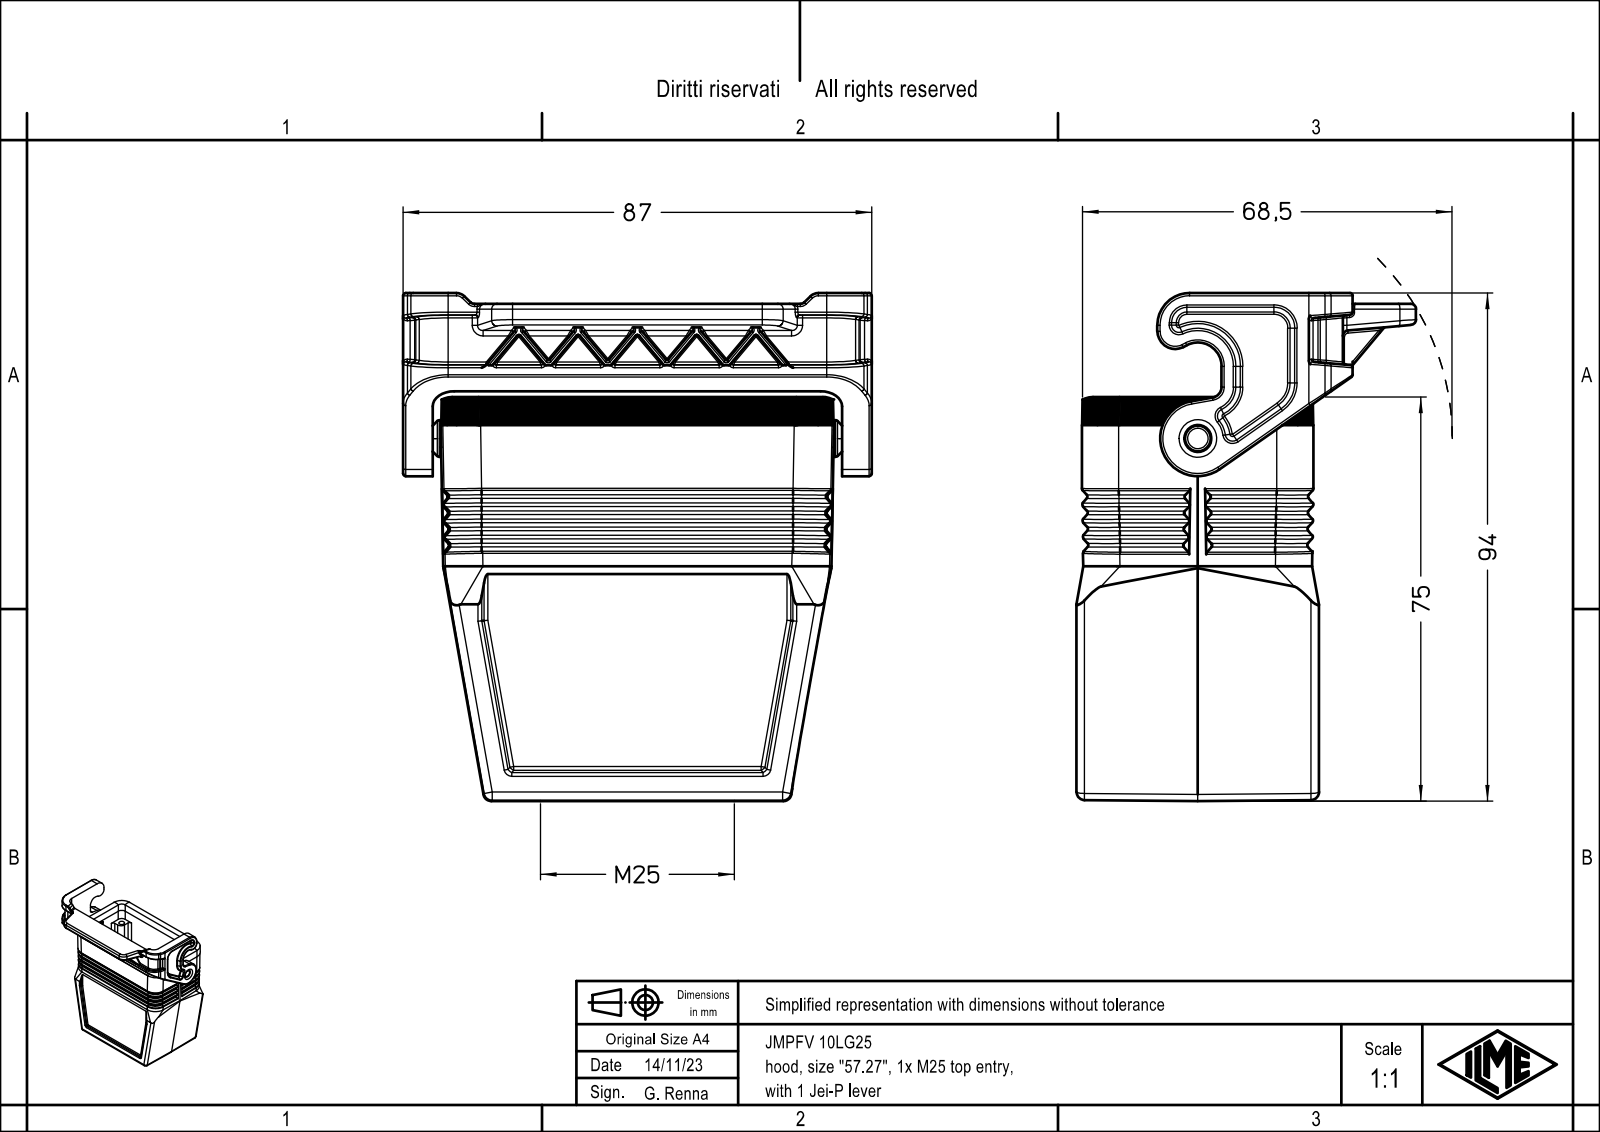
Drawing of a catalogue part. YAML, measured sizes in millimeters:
part_name: "JMPFV 10LG25"
step_written_by: "Creo Elements/Direct Modeling 20.1B 02-Apr-2019 (C) Parametric Technology GmbH (AUTOMOTIVE_DESIGN)"
units: millimeters
bodies: {solids: 1, faces: 998, planar: 269, cylindrical: 355, other: 374}
overall_size: [94.25, 87, 63]
volume: 88937
surface_area: 44343
round_holes:
  - {diameter: 3, count: 4}
  - {diameter: 3.5, count: 4}
  - {diameter: 4.8, count: 1}
  - {diameter: 23.6, count: 1}
round_bosses_or_shafts:
  - {diameter: 6.8, count: 1}
partial_cylinders:
  - {radius: 0.5, count: 96}
  - {radius: 0.3, count: 71}
  - {radius: 1, count: 35}
  - {radius: 1.5, count: 24}
  - {radius: 0.33, count: 15}
  - {radius: 7, count: 13}
  - {radius: 3, count: 12}
  - {radius: 4, count: 8}
face_to_face_distances: [39.25, 3.75, 43, 1, 4.75, 7, 34.5, 38.25, 35.5, 2]
hole_center_spacings: [31.54, 27, 57, 63.07]
